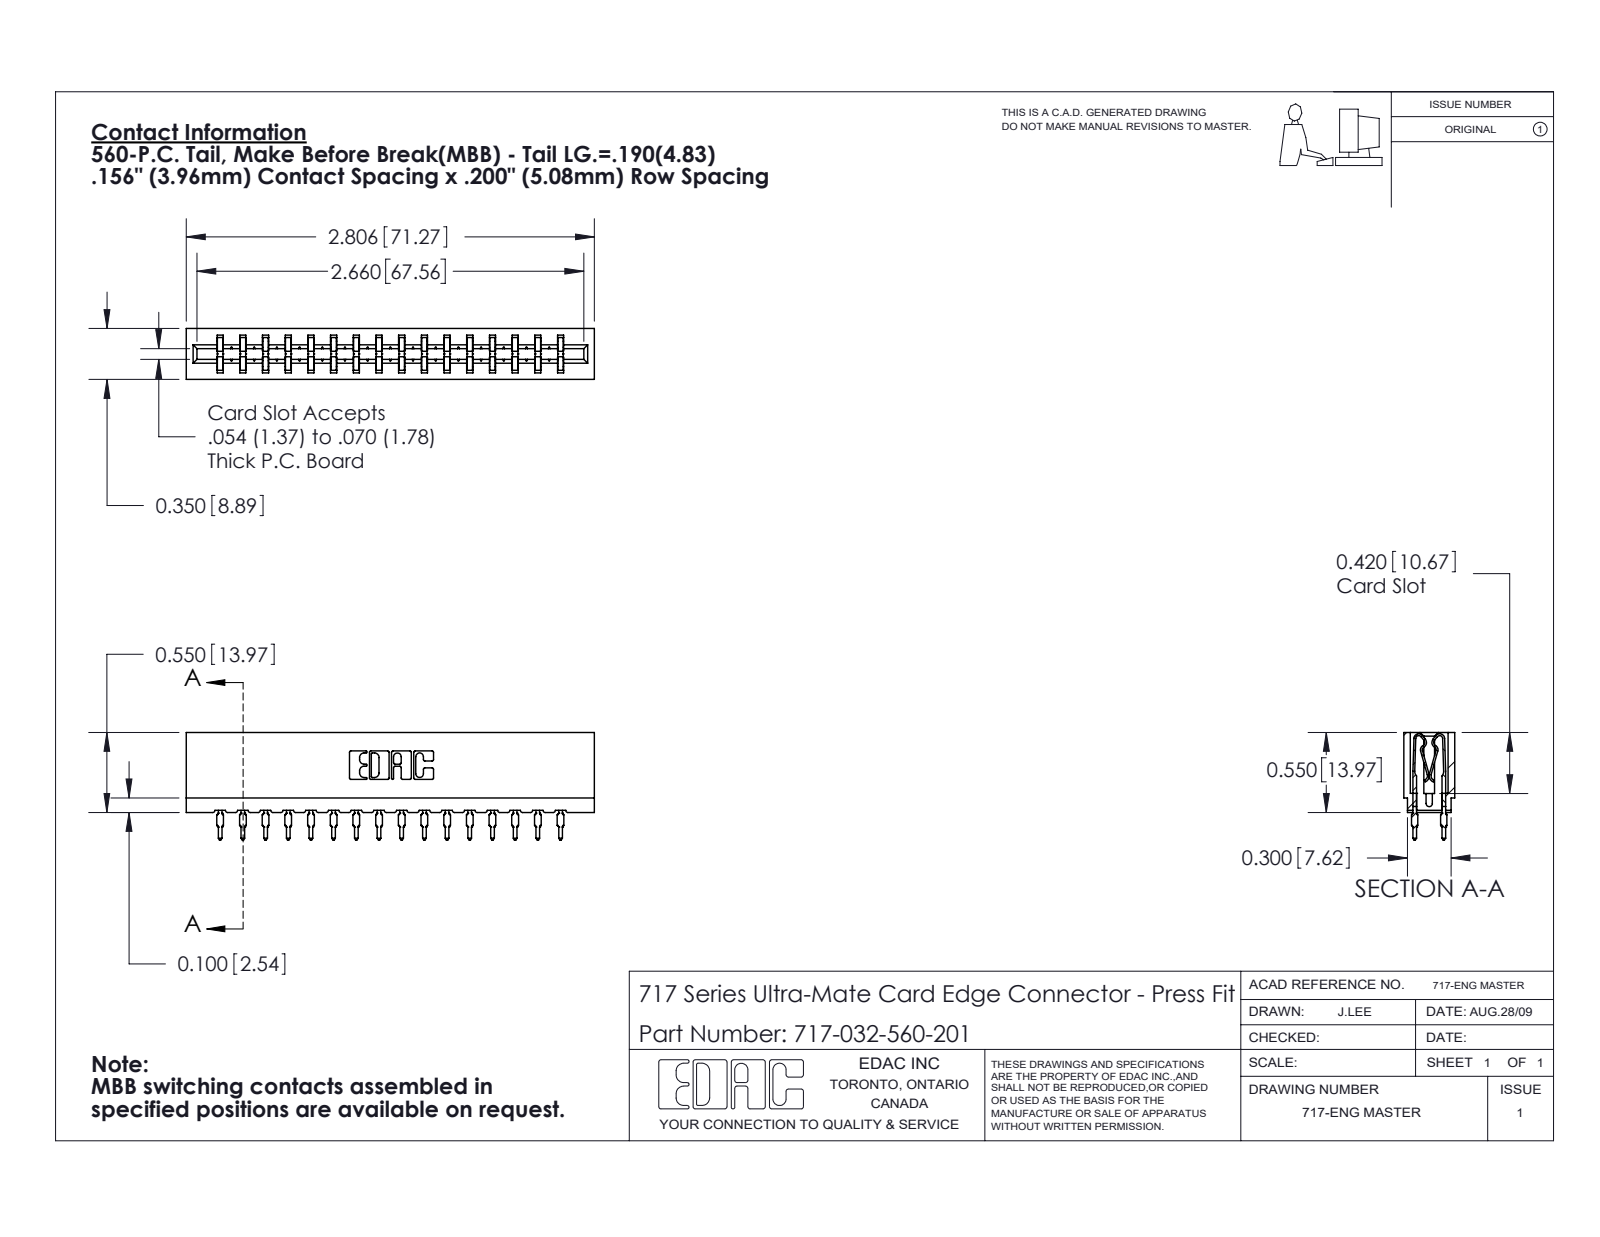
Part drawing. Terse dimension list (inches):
name: 717 Part_Insulator Option - 06; 717-032-560-201; 745-292-001_560
written by: SolidWorks 2020 (CONFIG_CONTROL_DESIGN)
unit: in
bodies: 33 solids, 3262 faces (1702 planar, 728 cylindrical, 832 other)
size: 2.806 × 0.739 × 0.35
volume: 0.391 in³; area: 15.51 in²
rounds: 64× R0.021, 32× R0.015, 22× R0.01, 8× R0.005, 8× R0.011, 6× R0.007, 6× R0.031, 3× R0.026
face distances: 0.212, 0.138, 0.35, 0.156, 0.468, 0.624, 0.063, 0.287, 0.076, 0.149
